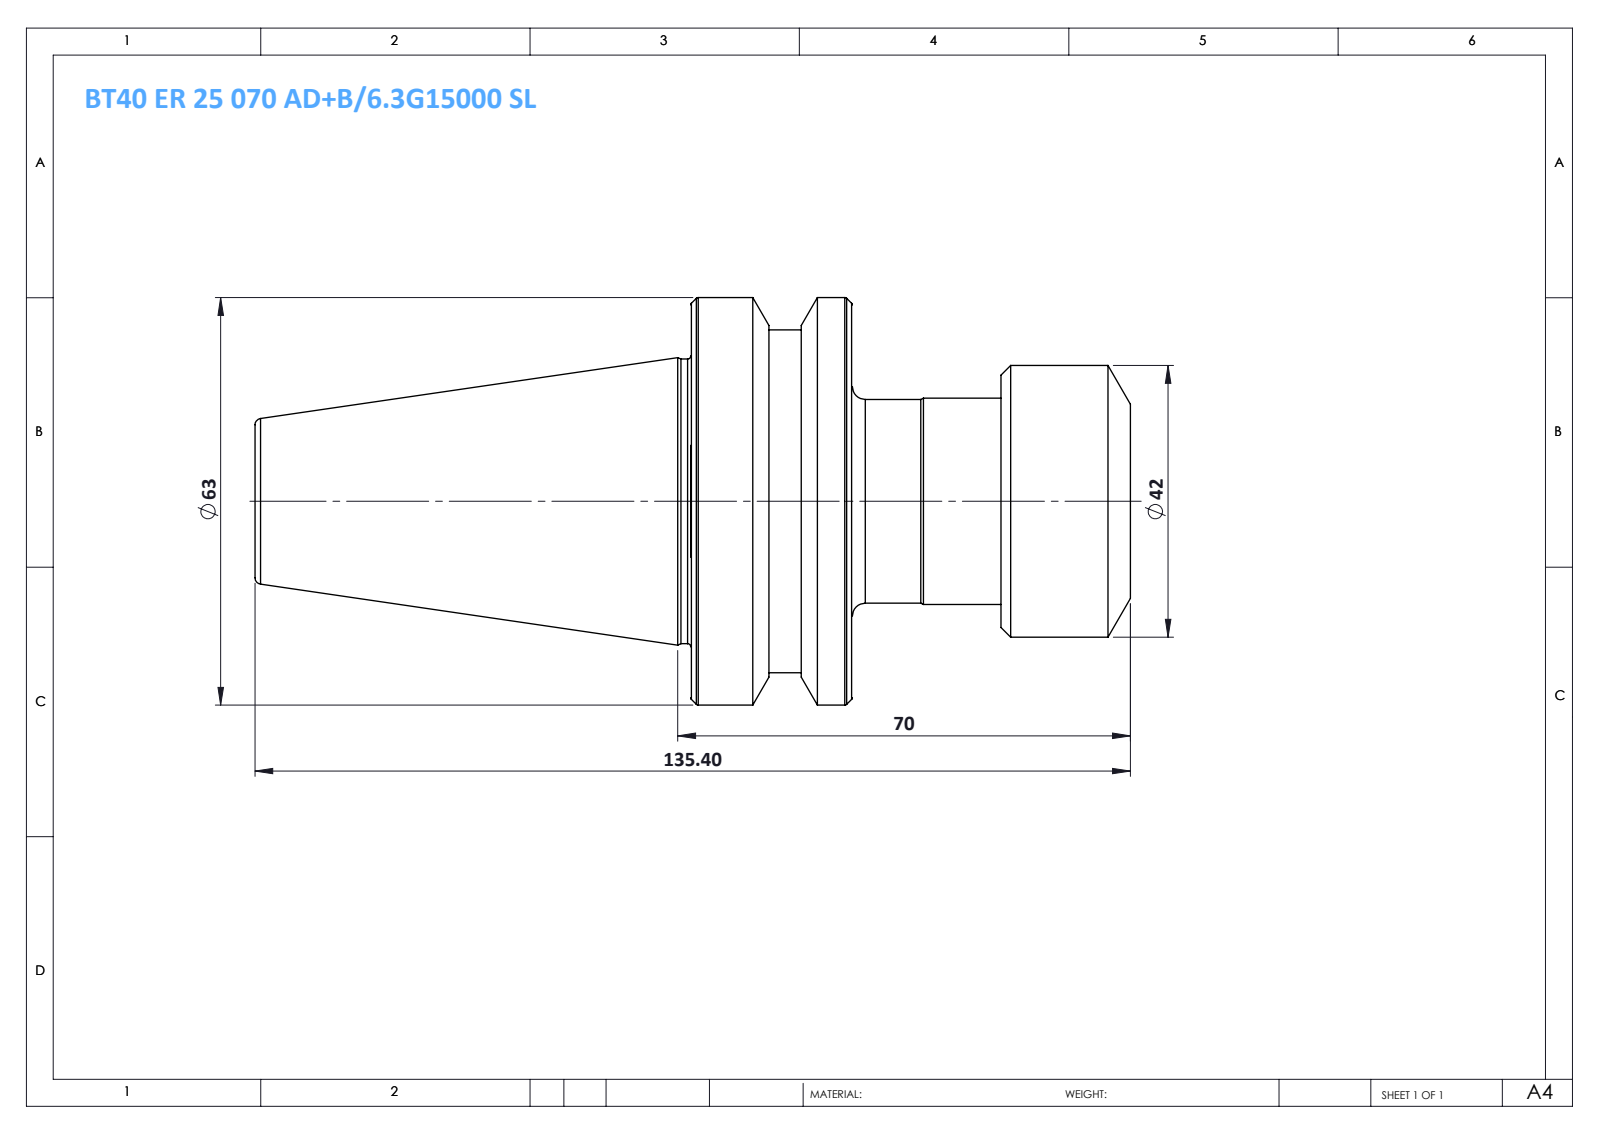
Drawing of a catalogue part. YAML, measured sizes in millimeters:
part_name: "BT40 ER 25 070 AD-6.3G15000 SL"
step_written_by: "SolidWorks 2014 (CONFIG_CONTROL_DESIGN)"
units: millimeters
bodies: {solids: 1, faces: 55, planar: 7, cylindrical: 14, other: 34}
overall_size: [135.4, 63, 63]
volume: 182915
surface_area: 24015
round_bosses_or_shafts:
  - {diameter: 63, count: 1}
  - {diameter: 53, count: 1}
  - {diameter: 44, count: 1}
  - {diameter: 42, count: 1}
  - {diameter: 31.9, count: 1}
  - {diameter: 31.5, count: 1}
face_to_face_distances: [25, 43, 68, 135.4, 92.4, 67.4, 20, 23, 48, 115.4]
